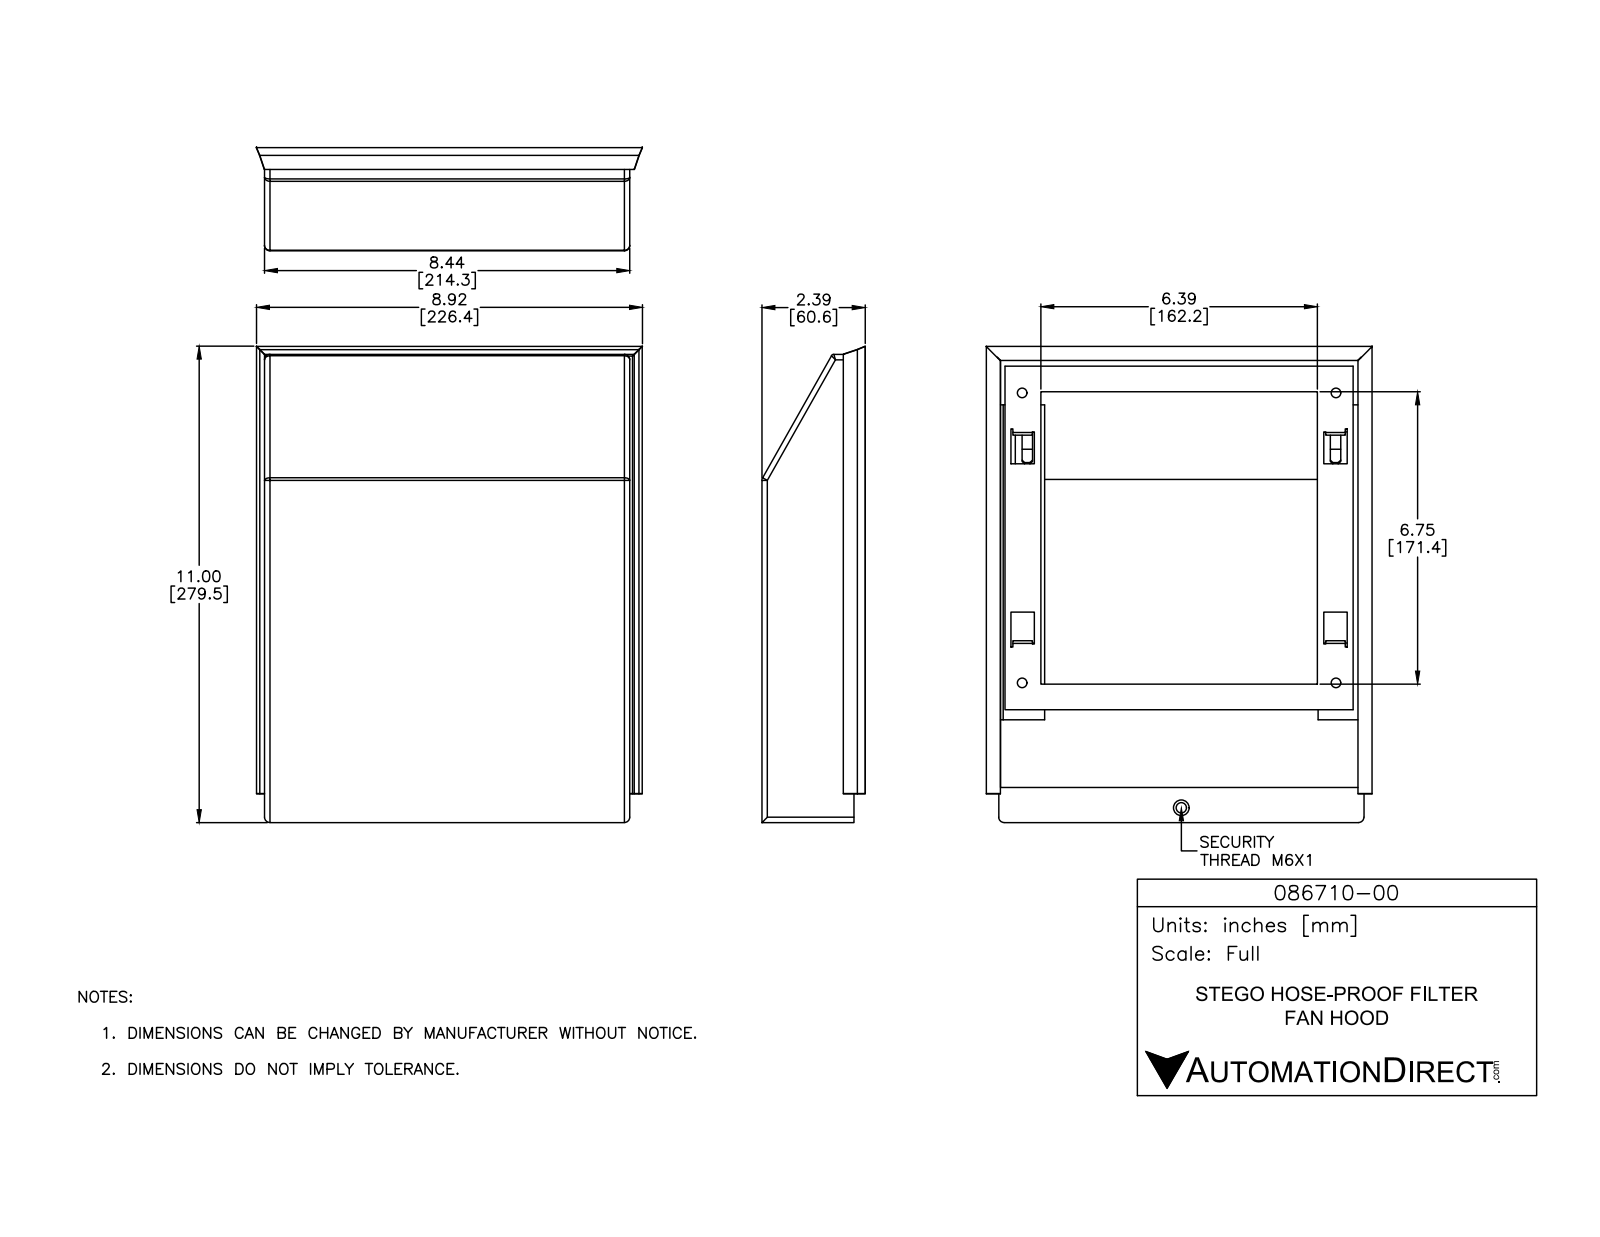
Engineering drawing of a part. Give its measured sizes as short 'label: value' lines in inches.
name: 086710-00; Gasket_1; 086710-00_2; 086710-00_1 (+2 more)
written by: SolidWorks 2017 (AUTOMOTIVE_DESIGN)
unit: in
bodies: 10 solids, 335 faces (233 planar, 98 cylindrical, 4 other)
size: 11.003 × 8.92 × 2.385
volume: 12.19 in³; area: 491.3 in²
holes: 4× ⌀0.22, 1× ⌀0.236, 1× ⌀0.36
bosses: 1× ⌀0.4
rounds: 38× R0.159, 9× R0.125, 5× R0.063, 4× R0.06, 3× R0.379
face distances: 0.04, 8.398, 8.357, 0.074, 2.01, 2.05, 8.438, 1.935, 1.976, 0.08
hole spacings: 6.697, 7.25, 9.87, 4.591, 4.675, 10.226, 10.264
